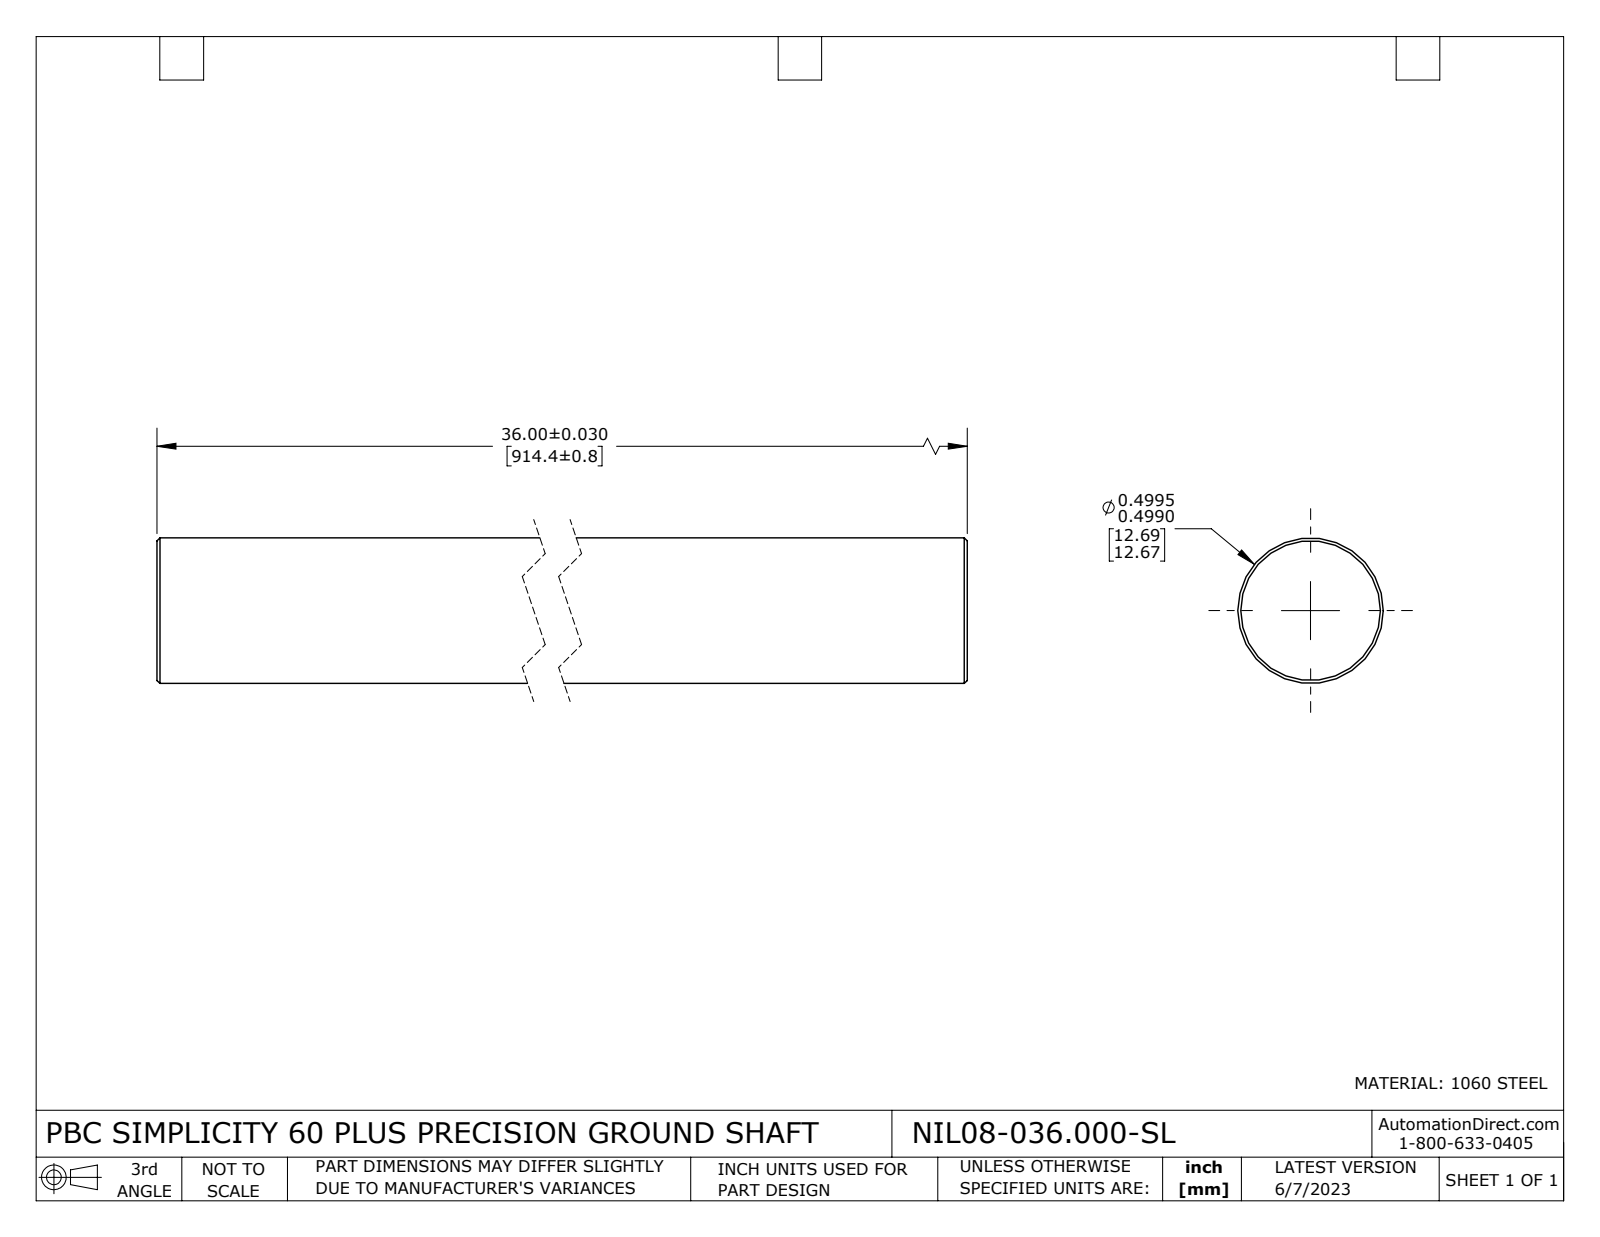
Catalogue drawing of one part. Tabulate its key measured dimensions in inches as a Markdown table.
| quantity | value |
| --- | --- |
| part name | NIL08-036.000-SL |
| STEP written by | SolidWorks 2021 (CONFIG_CONTROL_DESIGN) |
| units | inches |
| bodies | 1 solid, 8 faces (2 planar, 2 cylindrical, 4 other) |
| overall size | 36 × 0.5 × 0.5 |
| volume | 7.068 in³ |
| surface area | 56.92 in² |
| round bosses / shafts (diameter × count) | 0.5 × 1 |
| main face-to-face distances | 36 |
